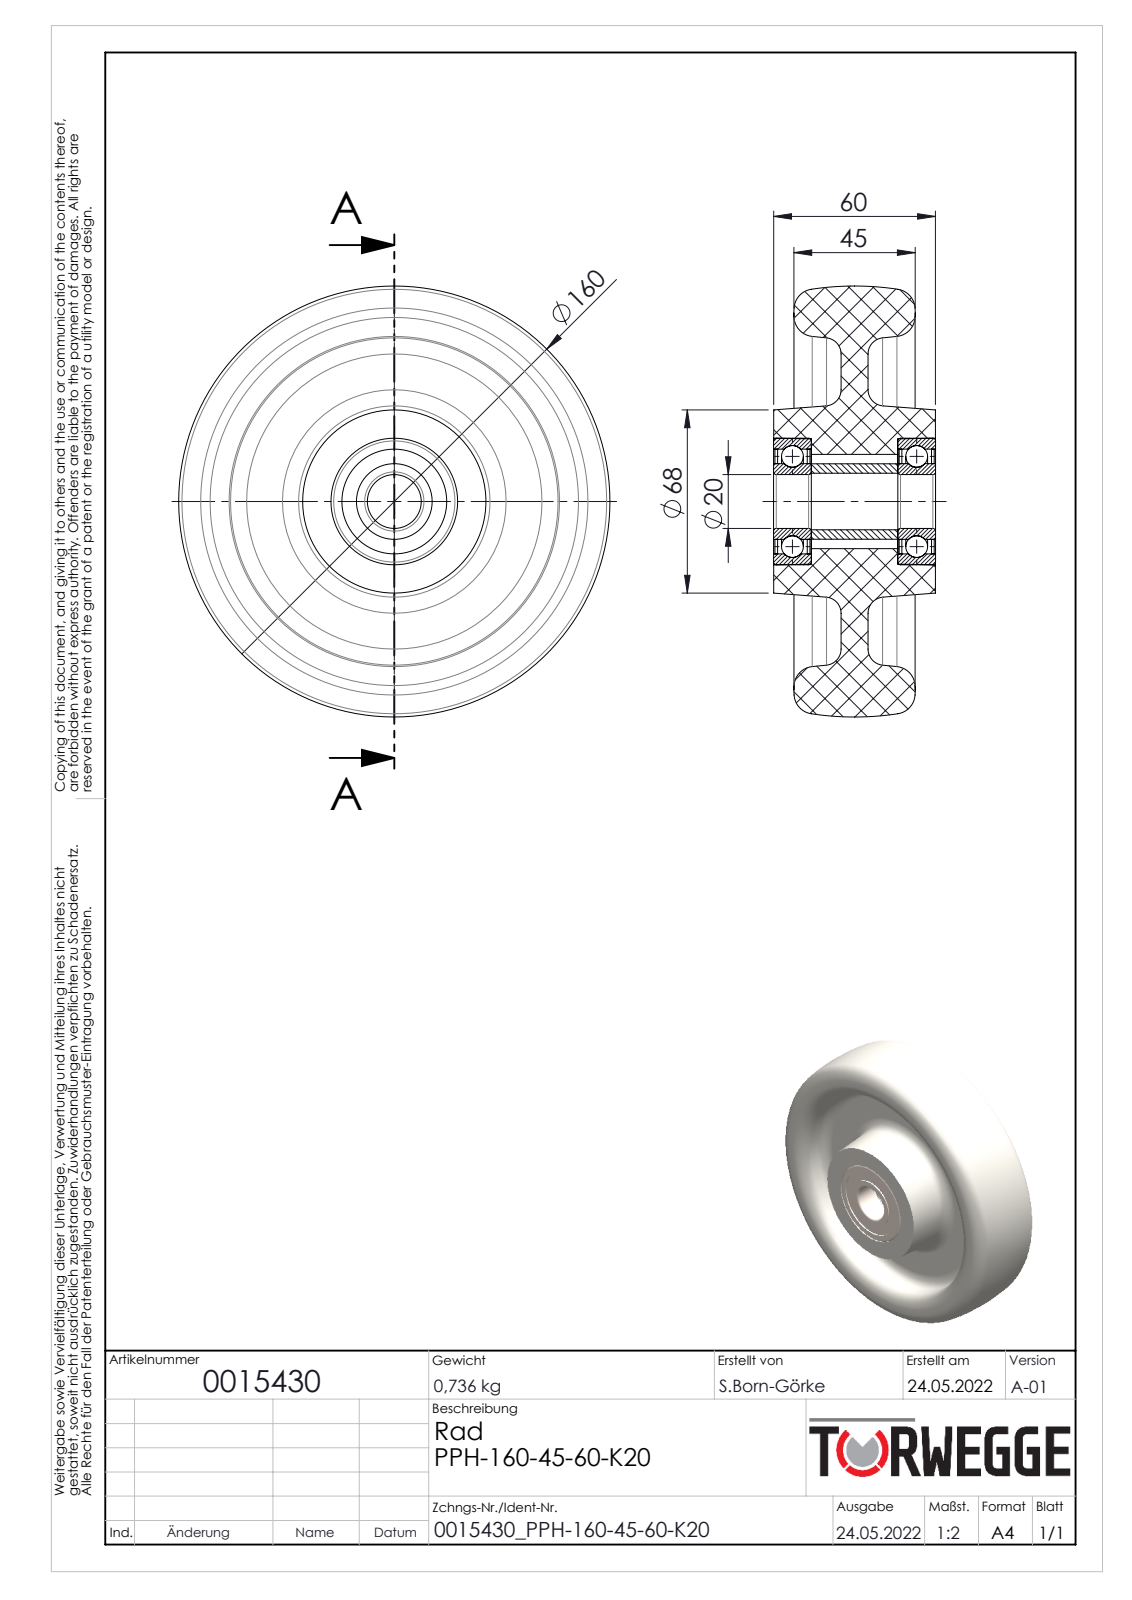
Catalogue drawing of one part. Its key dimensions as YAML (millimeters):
part_name: "0015430"
step_written_by: "SolidWorks 2020 (AUTOMOTIVE_DESIGN)"
units: millimeters
bodies: {solids: 12, faces: 142, planar: 24, cylindrical: 46, other: 72}
overall_size: [160, 160, 60.1]
volume: 624928
surface_area: 113182
round_holes:
  - {diameter: 20, count: 1}
  - {diameter: 21, count: 1}
  - {diameter: 28.1, count: 1}
  - {diameter: 35, count: 1}
  - {diameter: 38.9, count: 1}
round_bosses_or_shafts:
  - {diameter: 47, count: 1}
  - {diameter: 28, count: 1}
face_to_face_distances: [10, 25, 35, 46.1, 46.05, 14, 11, 0.5, 1.5, 12.5]
